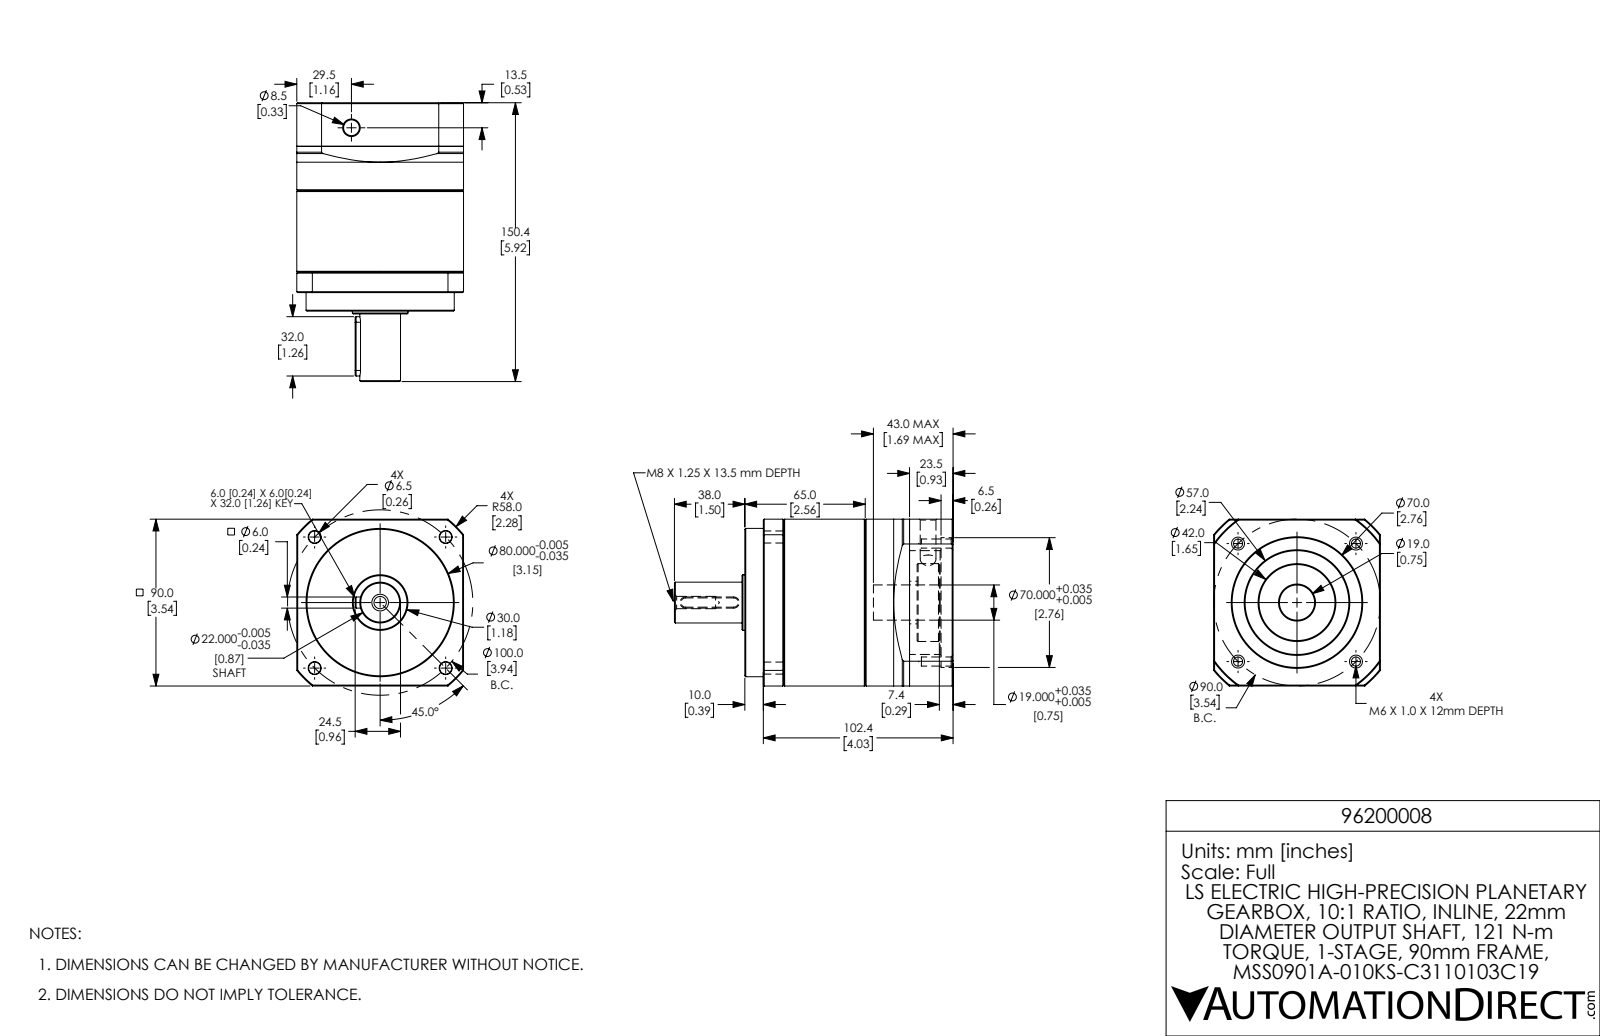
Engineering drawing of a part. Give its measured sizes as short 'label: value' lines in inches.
name: MSS0901A-C3110103
written by: SolidWorks 2017 (AUTOMOTIVE_DESIGN)
unit: in
bodies: 3 solids, 183 faces (46 planar, 54 cylindrical, 83 other)
size: 5.921 × 3.543 × 3.543
volume: 43.55 in³; area: 139.9 in²
holes: 4× ⌀0.256, 2× ⌀0.194, 2× ⌀0.194, 1× ⌀0.262, 1× ⌀0.335, 1× ⌀0.748, 1× ⌀2.205, 1× ⌀2.756
bosses: 1× ⌀3.543, 1× ⌀3.15, 1× ⌀1.654, 1× ⌀1.181, 1× ⌀0.906, 1× ⌀0.866
rounds: 2× R0.118, 1× R2.165, 1× R2.283
face distances: 0.941, 3.543, 3.5, 2.559, 0.925, 1.866, 4.425, 4.031, 3.106, 2.165
hole spacings: 2.648, 2.784, 0.197, 0.197, 1.771, 1.772, 1.969, 2.505
